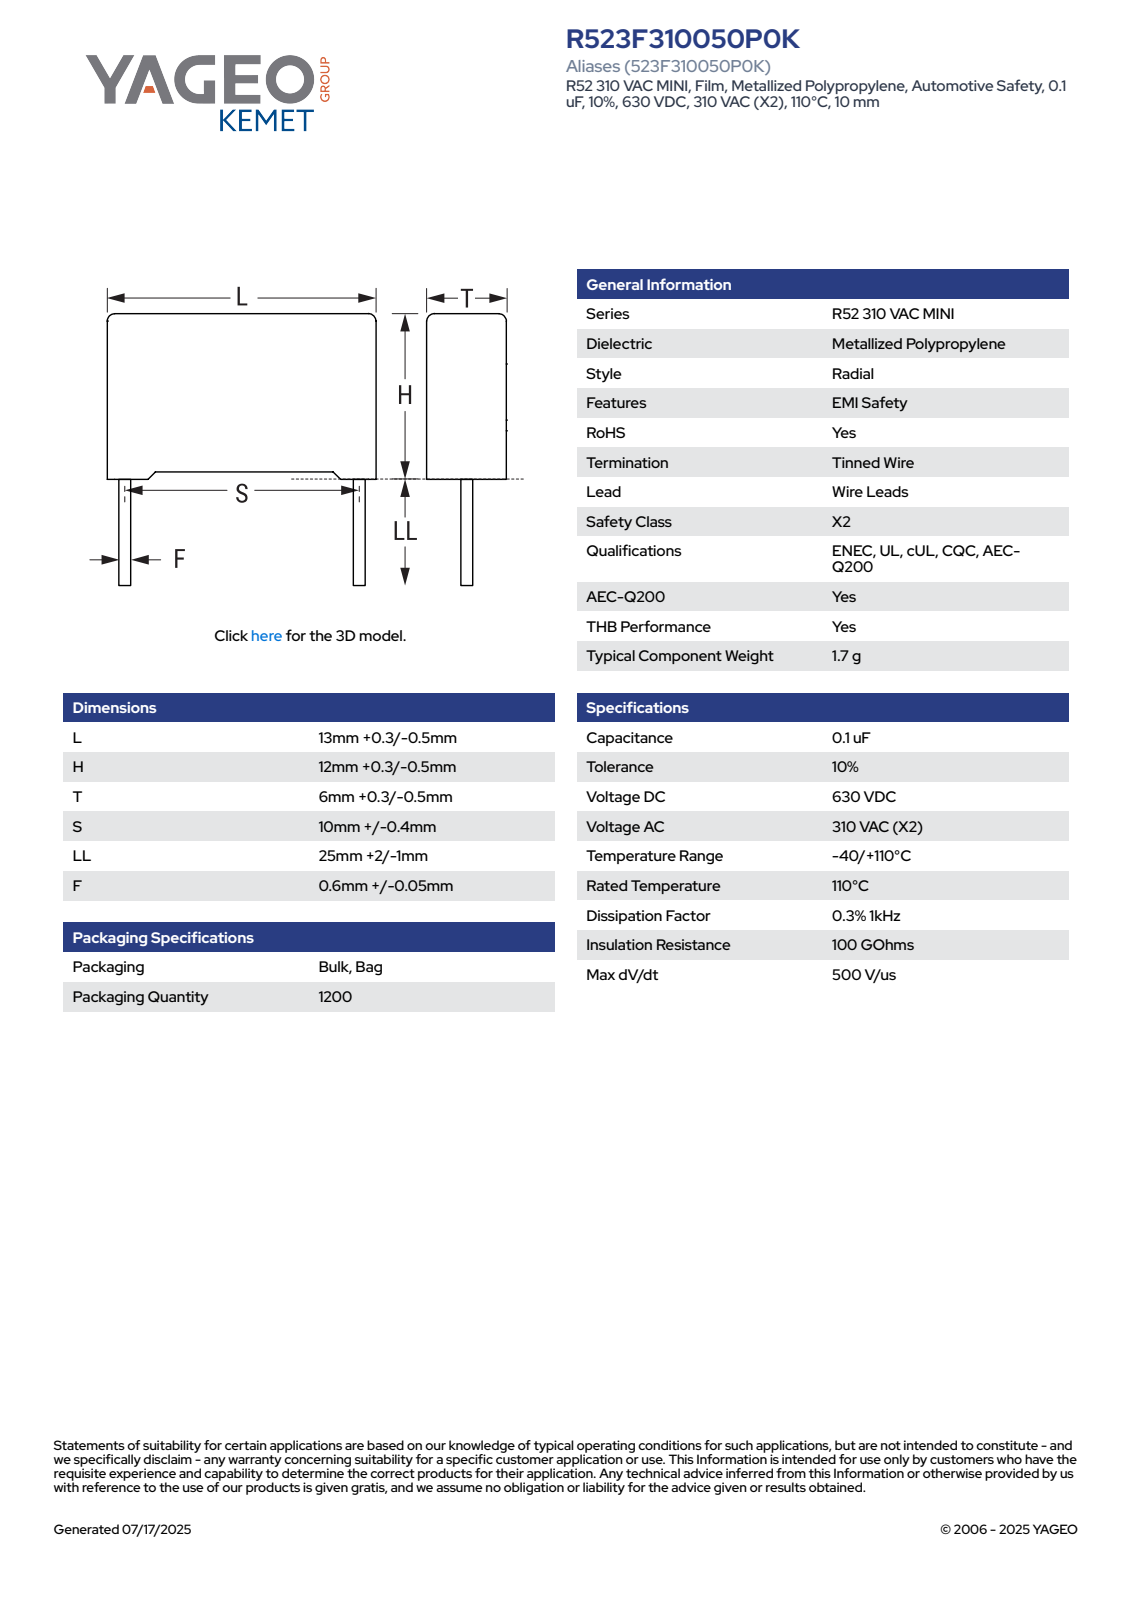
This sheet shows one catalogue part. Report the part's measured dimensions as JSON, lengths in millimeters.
{"part_name": "CFR_RB2_13X12X6_L13.3H12.3T6.3S10LL27F0.65", "step_written_by": "SolidWorks 2021 (AUTOMOTIVE_DESIGN)", "units": "millimeters", "bodies": {"solids": 4, "faces": 85, "planar": 77, "cylindrical": 8, "other": 0}, "overall_size": [39.3, 13.3, 6.3], "volume_mm3": 994, "surface_area_mm2": 784, "round_bosses_or_shafts": [[0.65, 2]], "partial_cylinders_radius": [[0.5, 4]], "face_to_face_distances": [6.3, 13.3, 11.55, 0.44, 5.86, 0.75, 12.3, 12.86, 5.42, 0.42]}
